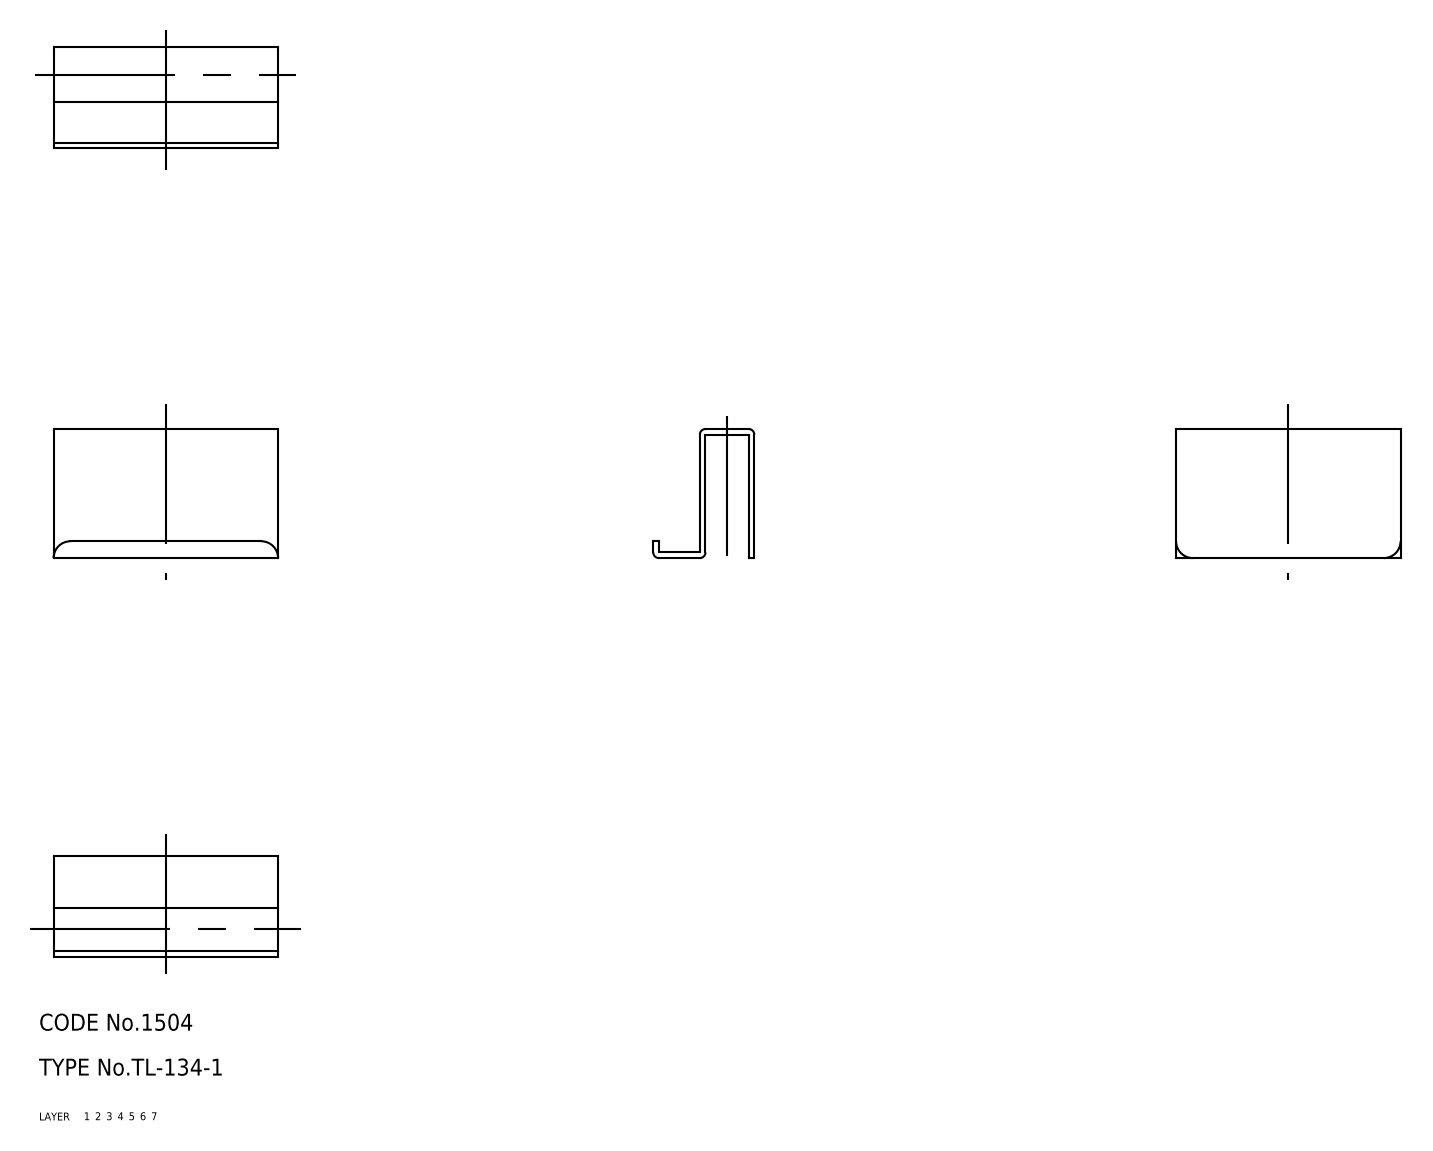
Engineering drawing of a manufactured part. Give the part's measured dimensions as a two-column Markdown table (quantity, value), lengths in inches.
| quantity | value |
| --- | --- |
| part name | keeper |
| STEP written by | CADfix (AUTOMOTIVE_DESIGN) |
| units | inches |
| bodies | 1 solid, 22 faces (0 planar, 0 cylindrical, 22 other) |
| overall size | 1.575 × 0.906 × 0.709 |
| volume | 0.154 in³ |
| surface area | 8.125 in² |
